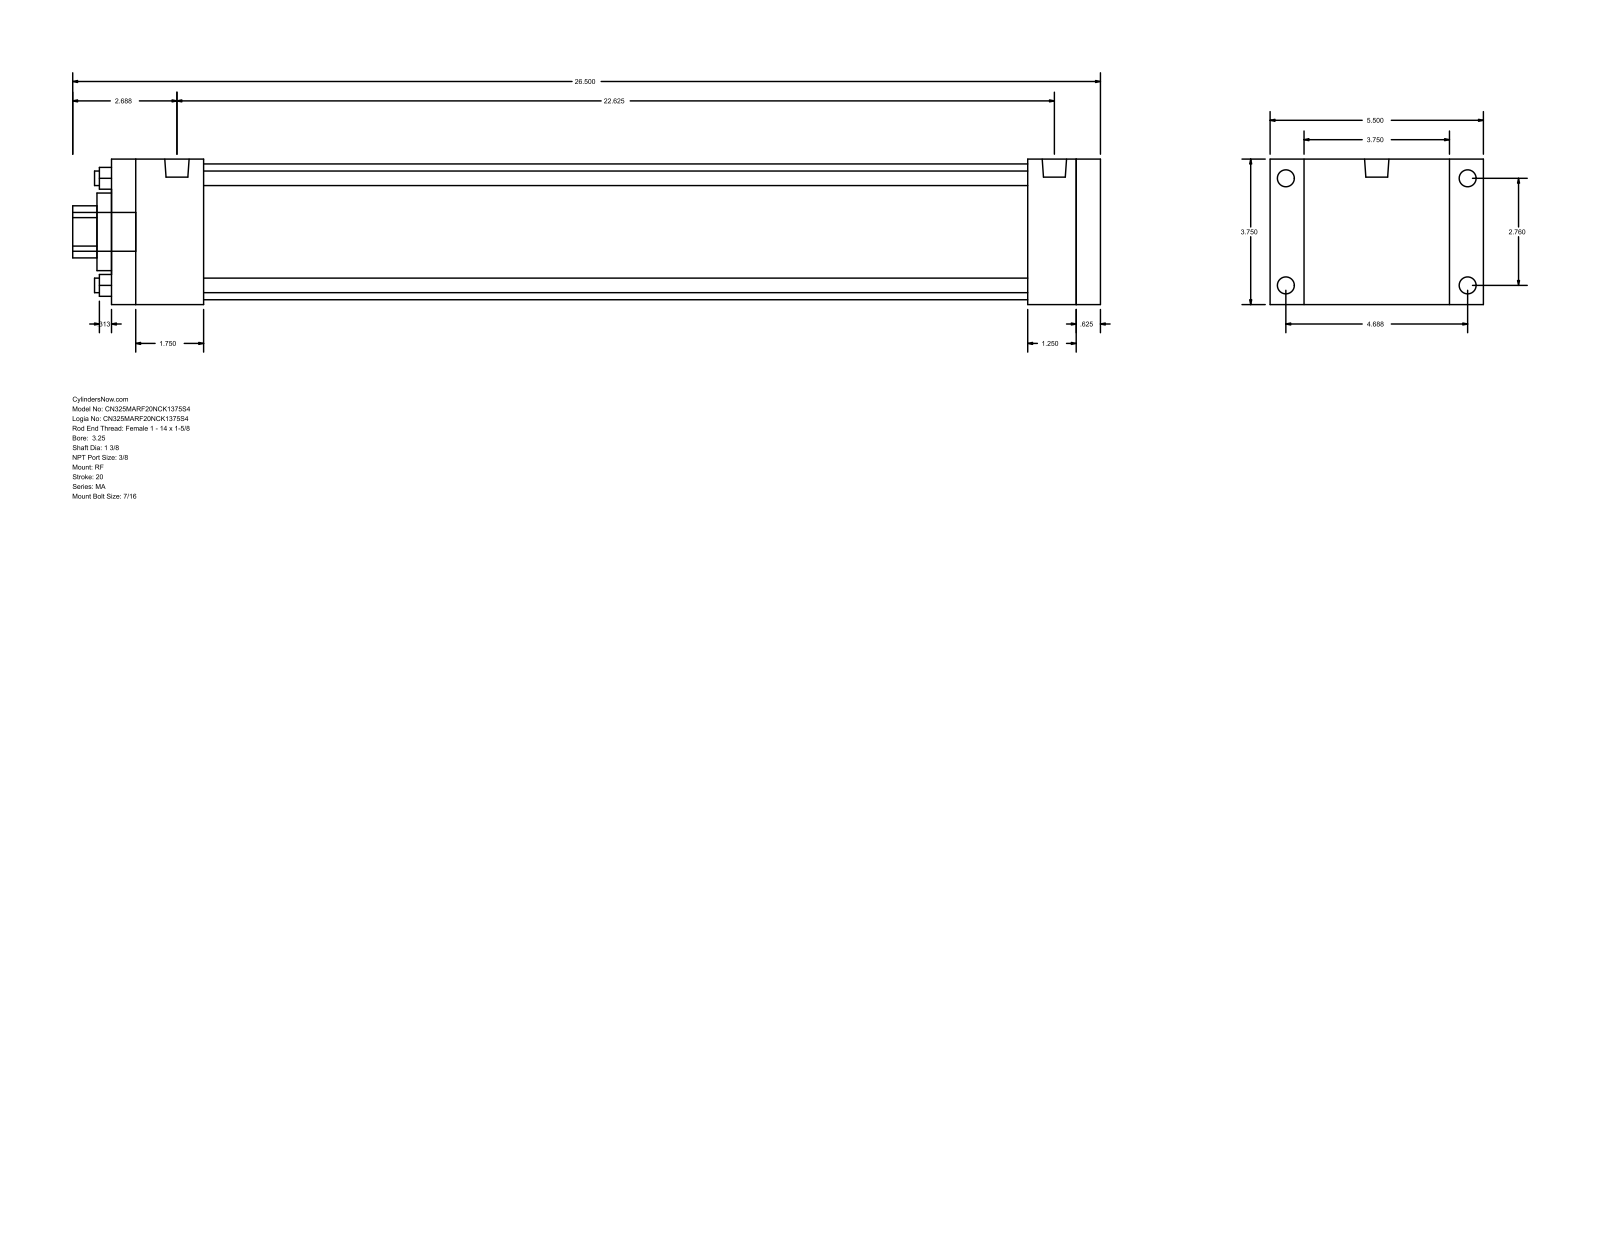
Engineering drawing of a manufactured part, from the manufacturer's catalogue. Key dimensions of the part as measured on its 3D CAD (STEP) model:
Part name (STEP PRODUCT): MA_RF__0325_1.375
STEP written by: GSSL Pune (CONFIG_CONTROL_DESIGN)
Units: millimetres
Bodies: 0 solids, 92 faces (64 planar, 28 cylindrical, 0 other)
Overall size (bounding box): 673.1 × 139.7 × 95.25
Round holes (diameter × count): ⌀9.53 ×4, ⌀34.92 ×1, ⌀50.8 ×1, ⌀88.9 ×1
Round bosses / shafts (diameter × count): ⌀11.11 ×8, ⌀15.93 ×2, ⌀25.4 ×1
Partial cylindrical surfaces — rounded edges, fillets, slot ends (radius × count): R17.06 ×1
Main face-to-face distances: 95.24, 647.7, 15.87, 631.83, 22.23, 117.47, 600.08, 31.75, 47.62, 60.32
Hole centre spacings: 49.57, 70.1, 99.14
